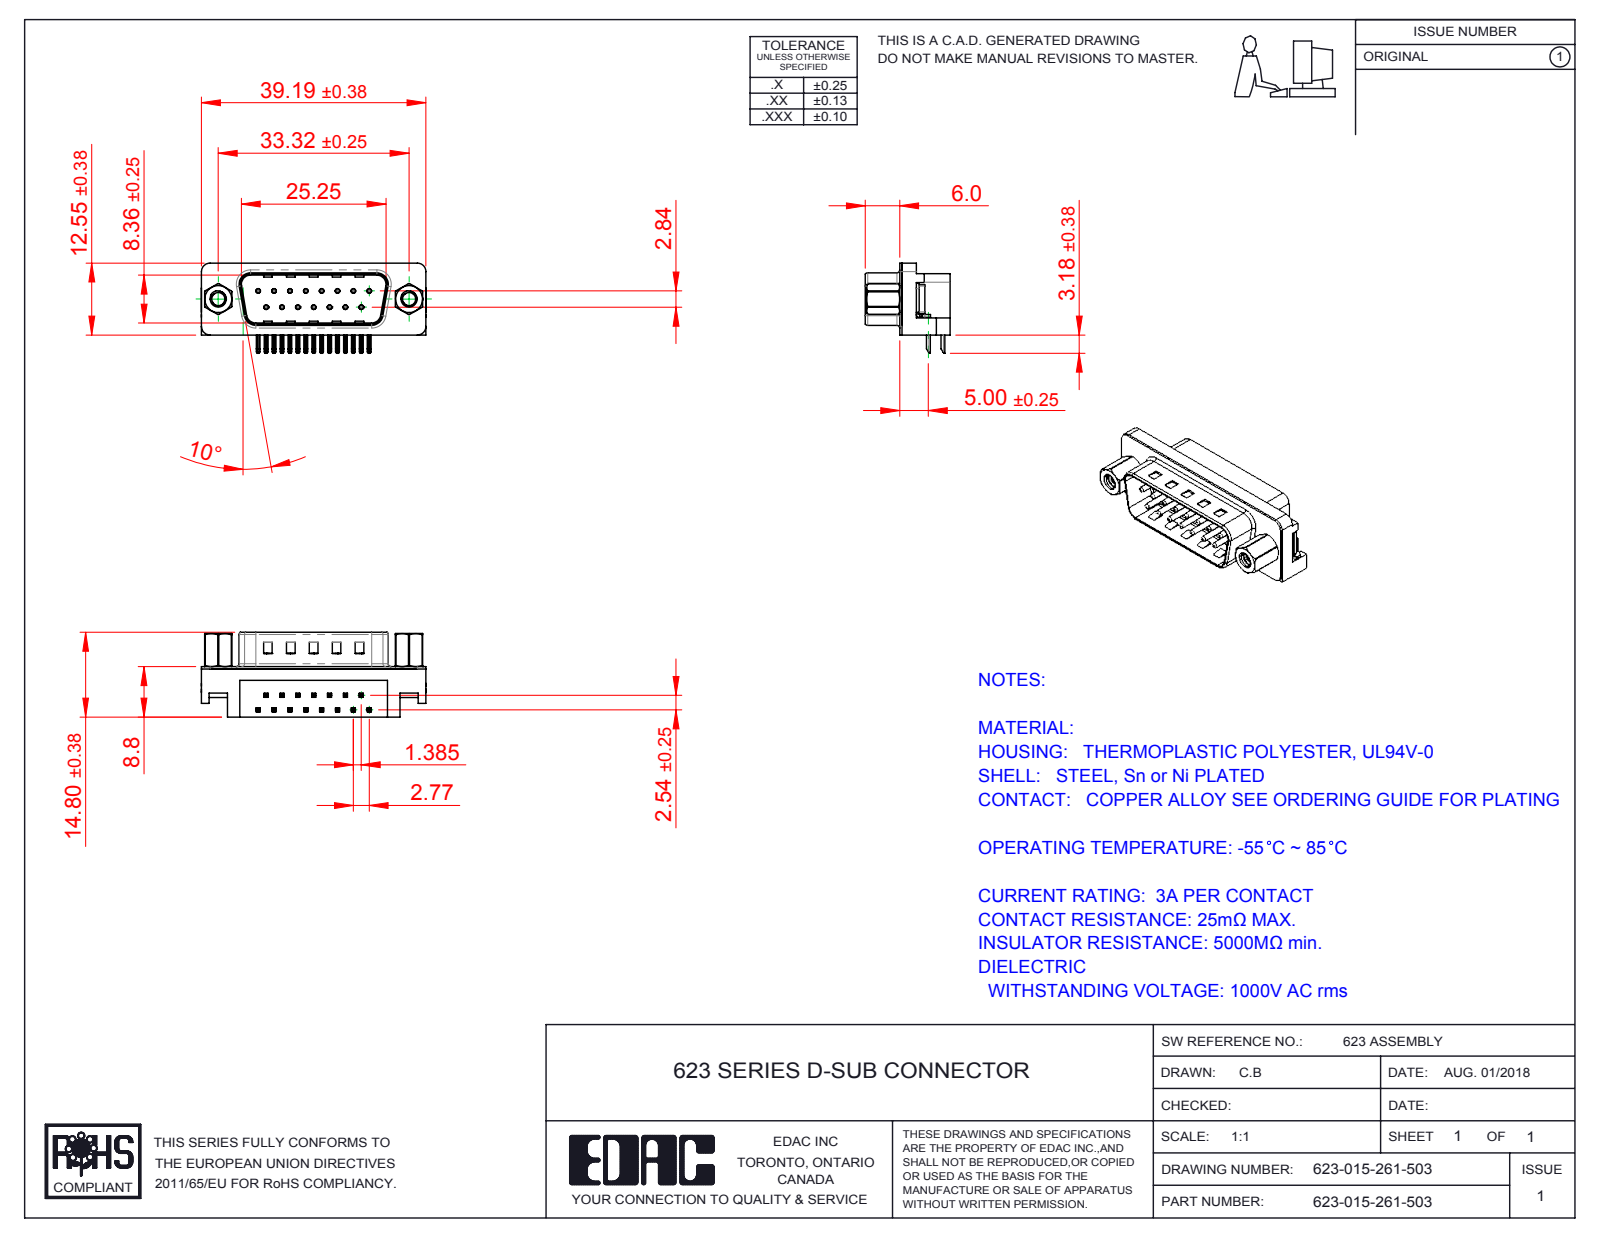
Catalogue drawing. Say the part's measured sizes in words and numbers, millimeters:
The part is named "623 4-40 Threaded Rivet; 623 4-40 Hex Standoff 5; 623 Non Board Mount; 623 Shell_15 Socket (+4 more)". Its 3-D file was written by "SolidWorks 2016 (CONFIG_CONTROL_DESIGN)". It is 23 solids with 1591 faces: 915 planar, 503 cylindrical and 173 other. Overall it measures 39.22 by 15.73 by 14.8 millimeters. Its volume is 3 527 cubic millimeters and its surface area 5 355 square millimeters. Round holes: 15 of diameter 0.35, 15 of diameter 0.8, 2 of diameter 2.26, 2 of diameter 2.29, 2 of diameter 4, 2 of diameter 4.8, 2 of diameter 5. Round bosses or shafts: 15 of diameter 0.75, 2 of diameter 4.9, 2 of diameter 4.75, 2 of diameter 3.9, 2 of diameter 2.79. Partial cylindrical surfaces (rounded edges, fillets, slot ends): 68 of radius 0.25, 30 of radius 0.12, 16 of radius 1, 9 of radius 0.5, 6 of radius 1.5, 4 of radius 0.9, 4 of radius 1.6, 4 of radius 2. The main face-to-face distances are 0.4, 8.4, 8.8, 2.1, 1.7, 10.46, 10.86, 8.76, 5.9, 2.9. The hole center spacings are 3.16, 2.77, 5.54, 8.31, 11.08, 5.03, 5.04, 7.48.
